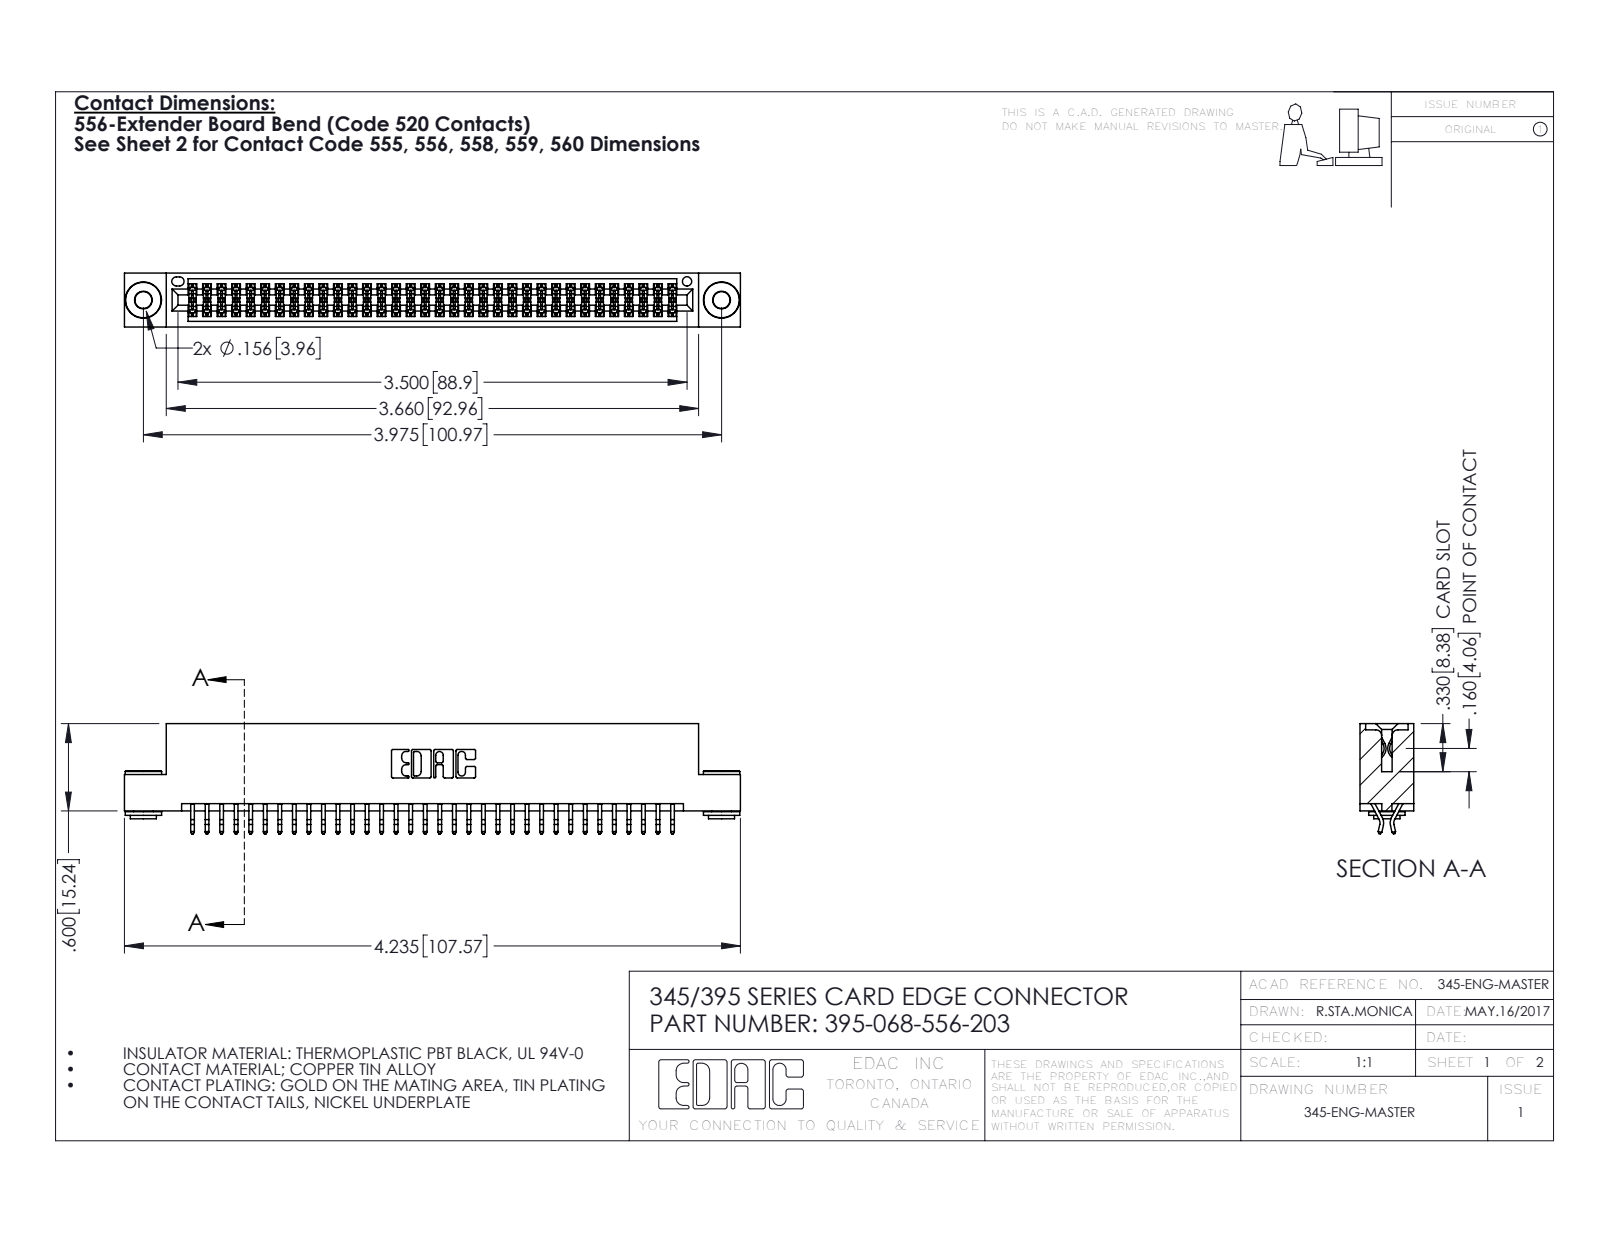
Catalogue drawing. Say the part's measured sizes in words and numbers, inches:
The part is named "345-292-001_556 Tail; 395-068-556-203; 345 Part_Flush Mounting Lugs - 0.156 Dia-TH; 345-250-002_345-250-002-102". Its 3-D file was written by "SolidWorks 2016 (CONFIG_CONTROL_DESIGN)". It is 71 solids with 3972 faces: 2606 planar, 1358 cylindrical and 8 other. Overall it measures 4.235 by 0.757 by 0.37 inches. Its volume is 0.634 cubic inches and its surface area 23.79 square inches. Round holes: 2 of diameter 0.116, 2 of diameter 0.156, 1 of diameter 0.064. Round bosses or shafts: 2 of diameter 0.25, 2 of diameter 0.18, 2 of diameter 0.136. Partial cylindrical surfaces (rounded edges, fillets, slot ends): 102 of radius 0.006, 22 of radius 0.01, 6 of radius 0.007, 6 of radius 0.031, 3 of radius 0.026, 2 of radius 0.01, 2 of radius 0.014, 2 of radius 0.019. The main face-to-face distances are 0.072, 0.298, 0.2, 0.37, 0.025, 0.098, 0.272, 0.225, 0.175, 0.149. The hole center spacings are 0.27, 3.74, 3.975.
